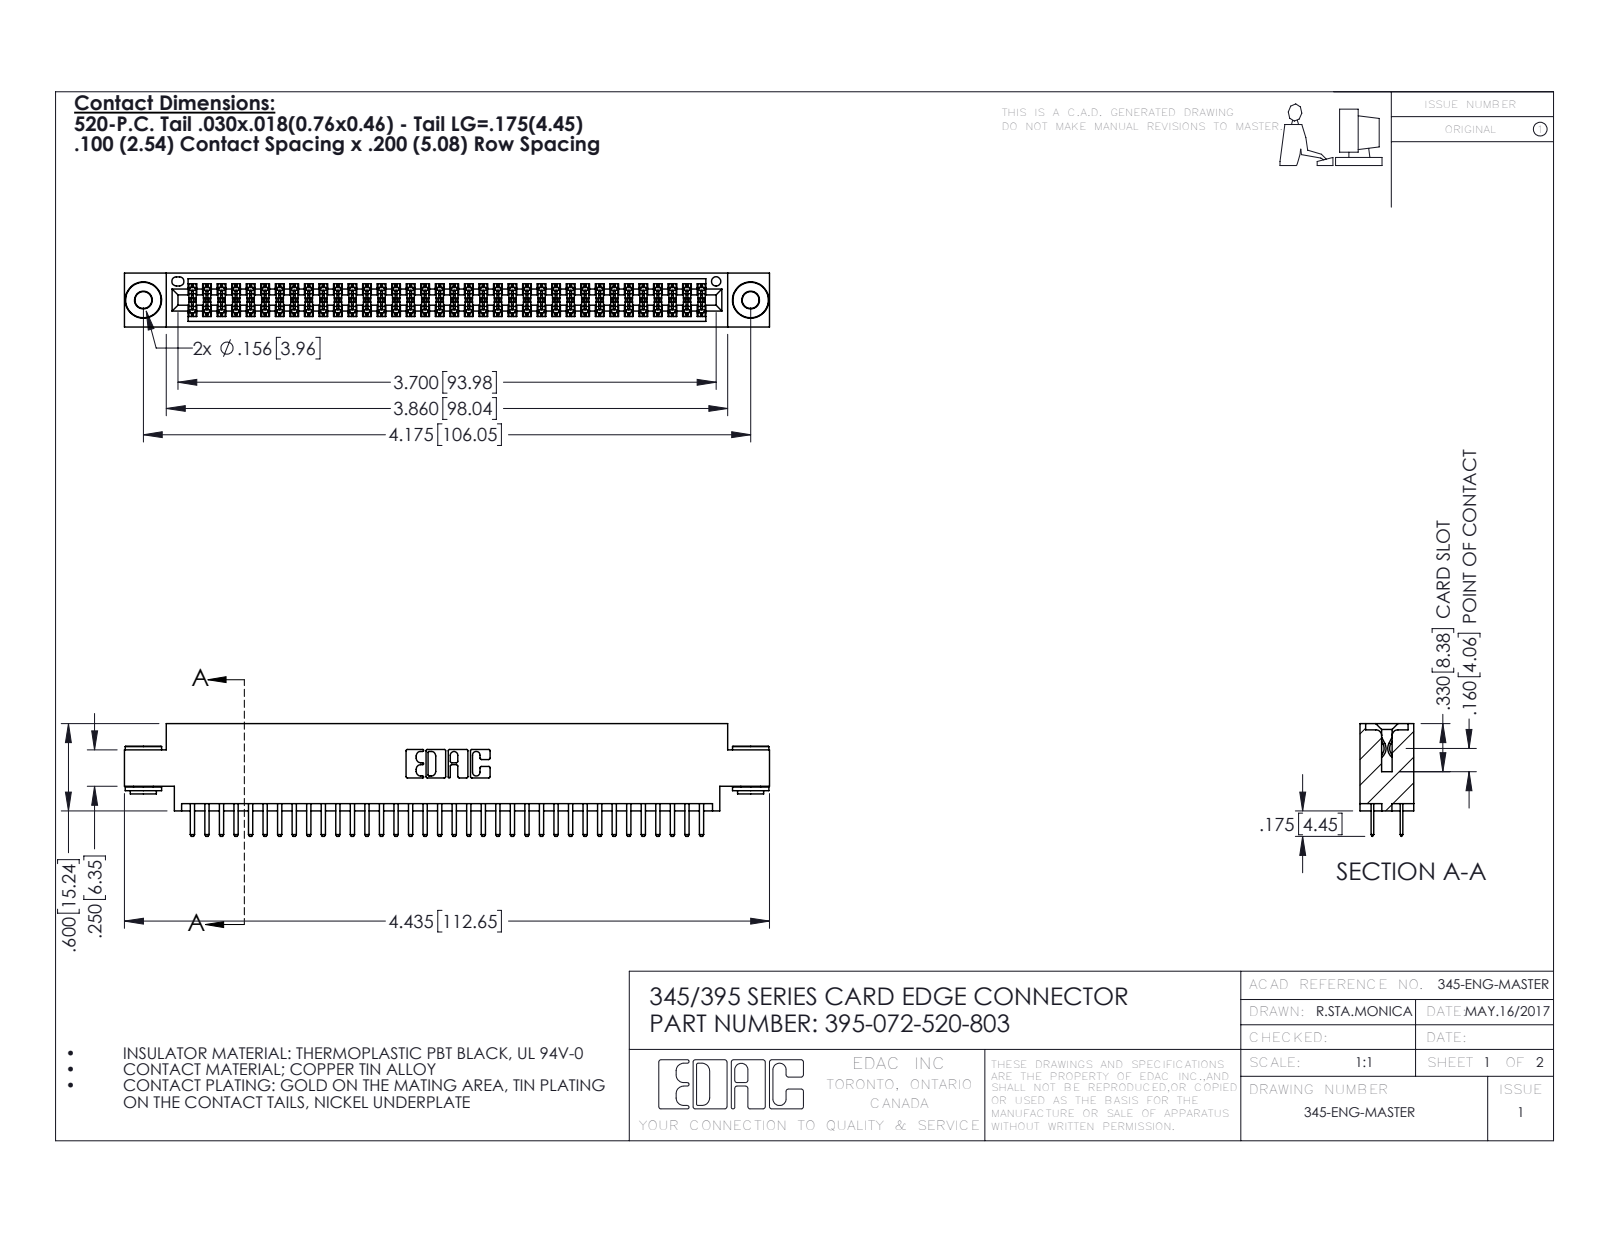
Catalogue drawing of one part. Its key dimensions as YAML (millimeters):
part_name: "345-292-001_345-293-120; 395-072-520-803; 345-250-002_345-250-002-102; 345 Part_0.170 Offset - 0.156 Dia-TH"
step_written_by: "SolidWorks 2016 (CONFIG_CONTROL_DESIGN)"
units: millimeters
bodies: {solids: 75, faces: 4056, planar: 2614, cylindrical: 1434, other: 8}
overall_size: [112.6, 19.7, 9.4]
volume: 10800
surface_area: 16070
round_holes:
  - {diameter: 2.9, count: 2}
  - {diameter: 4, count: 2}
  - {diameter: 1.6, count: 1}
round_bosses_or_shafts:
  - {diameter: 6.4, count: 2}
  - {diameter: 4.6, count: 2}
  - {diameter: 3.5, count: 2}
partial_cylinders:
  - {radius: 0.2, count: 108}
  - {radius: 0.3, count: 76}
  - {radius: 0.3, count: 22}
  - {radius: 0.2, count: 6}
  - {radius: 0.8, count: 6}
  - {radius: 0.7, count: 3}
  - {radius: 0.4, count: 2}
  - {radius: 0.5, count: 2}
face_to_face_distances: [1.8, 7.6, 5.1, 9.4, 2.5, 6.9, 0.6, 5.7, 4.4, 0.6]
hole_center_spacings: [6.9, 100.1, 106]
